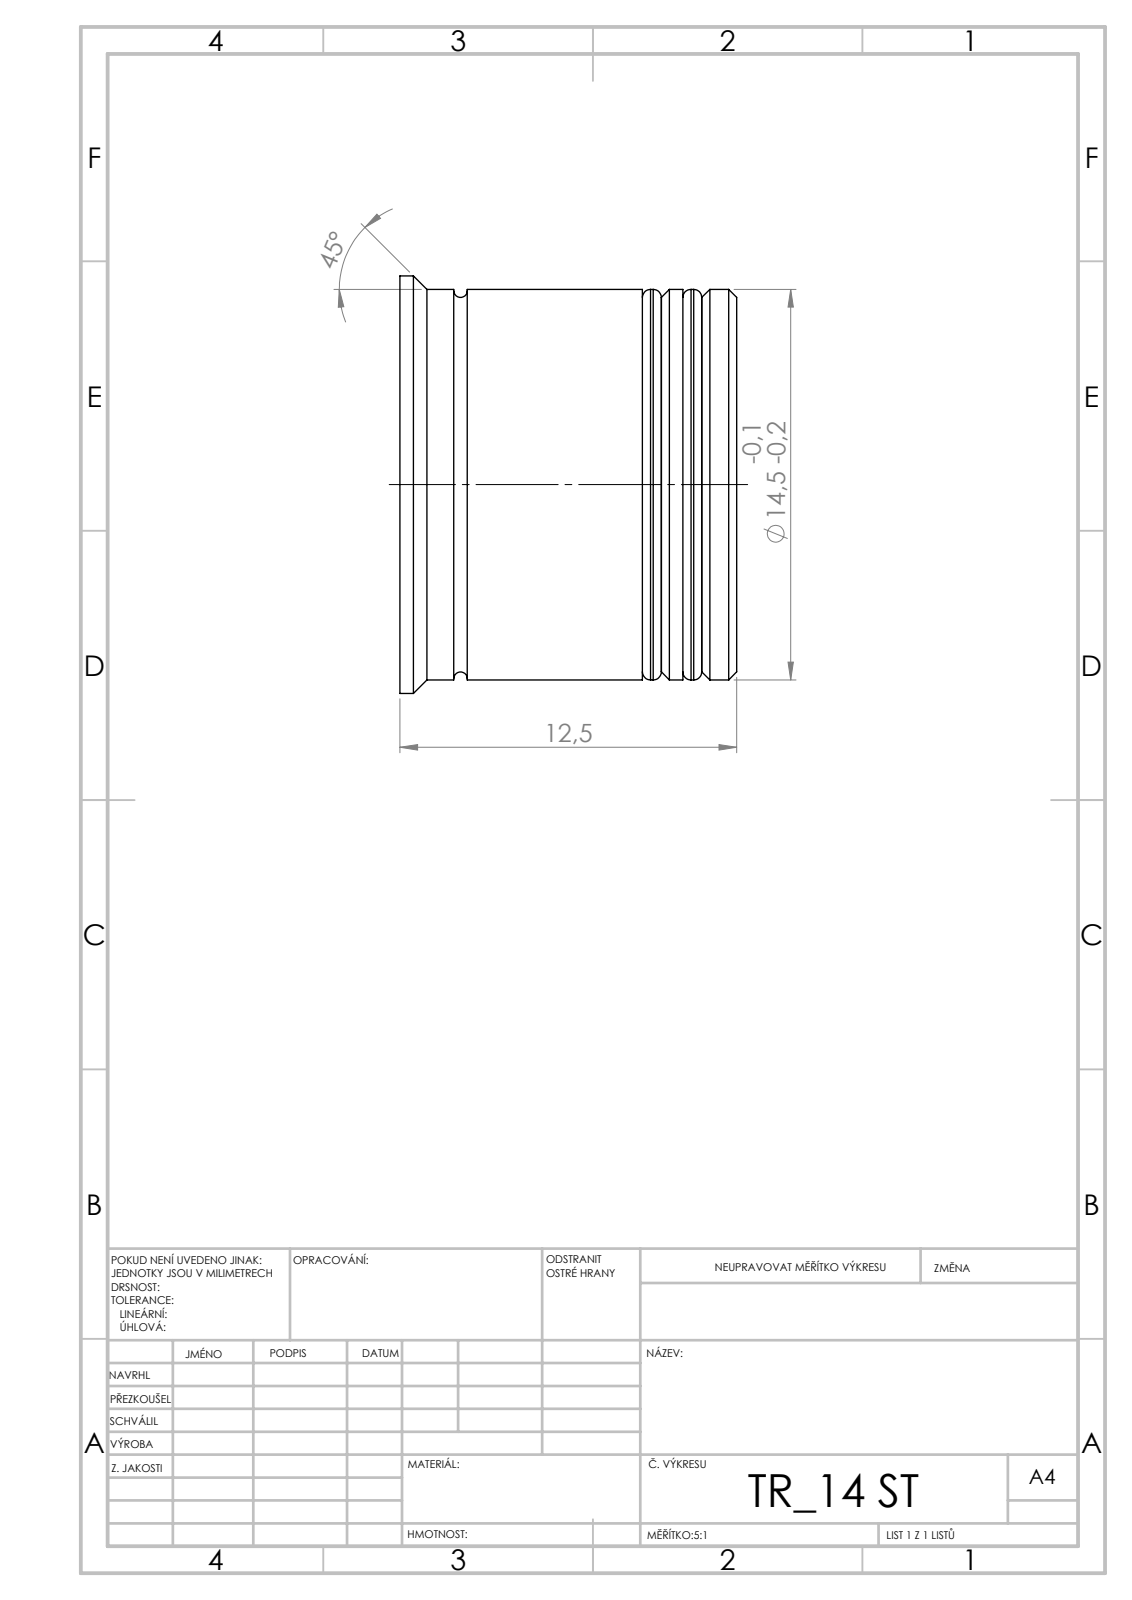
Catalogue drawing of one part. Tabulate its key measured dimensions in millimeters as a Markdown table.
| quantity | value |
| --- | --- |
| STEP written by | SolidWorks 2019 (CONFIG_CONTROL_DESIGN) |
| units | millimeters |
| bodies | 3 solids, 74 faces (29 planar, 25 cylindrical, 20 other) |
| overall size | 15.5 × 15.5 × 12.5 |
| volume | 2 153 mm³ |
| surface area | 1 779 mm² |
| round bosses / shafts (diameter × count) | 15.5 × 1, 14.5 × 1, 13.9 × 1, 11.5 × 1 |
| main face-to-face distances | 1.5, 0.7, 2, 11.5, 3.5, 1.3, 2.2, 2.8, 0.8, 8.7 |
